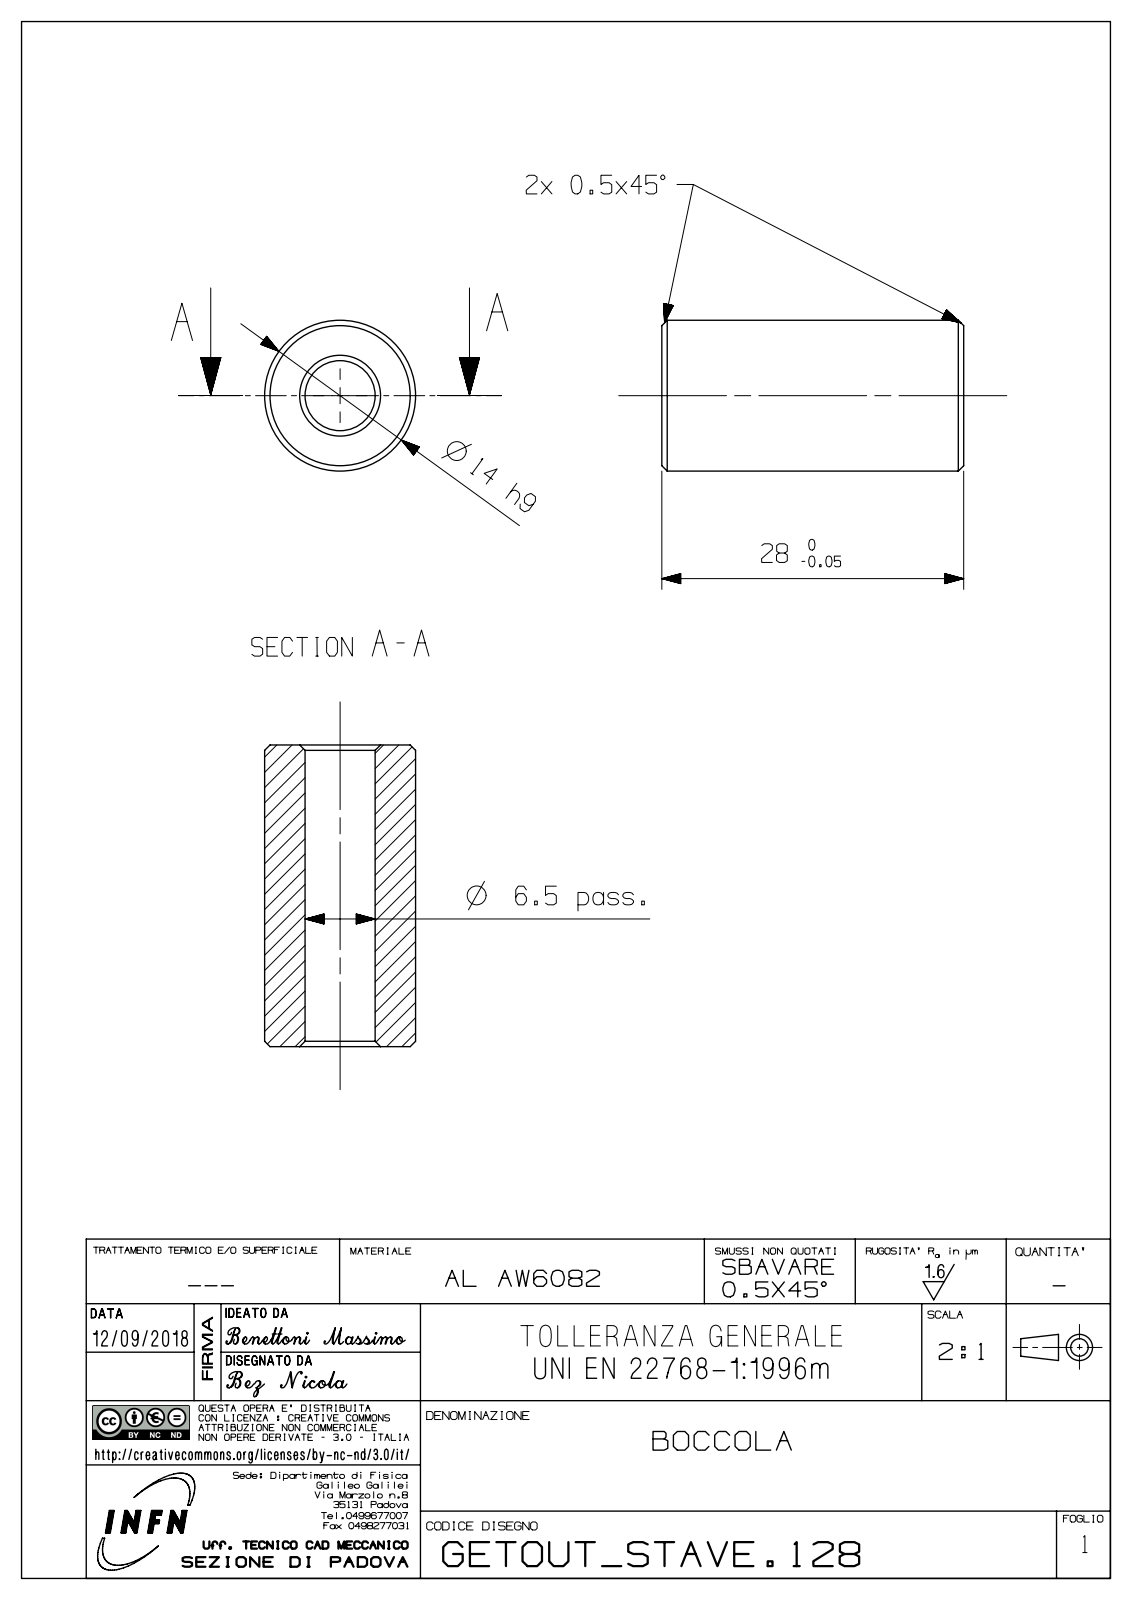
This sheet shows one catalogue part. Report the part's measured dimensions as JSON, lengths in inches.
{"part_name": "bez8324385A6v1b", "step_written_by": "SIEMENS PLM Software NX 12.0 (AUTOMOTIVE_DESIGN)", "units": "inches", "bodies": {"solids": 1, "faces": 8, "planar": 2, "cylindrical": 2, "other": 4}, "overall_size": [1.102, 0.551, 0.551], "volume_in3": 0.205, "surface_area_in2": 3.111, "round_holes": [[0.256, 1]], "round_bosses_or_shafts": [[0.551, 1]], "face_to_face_distances": [1.102]}
